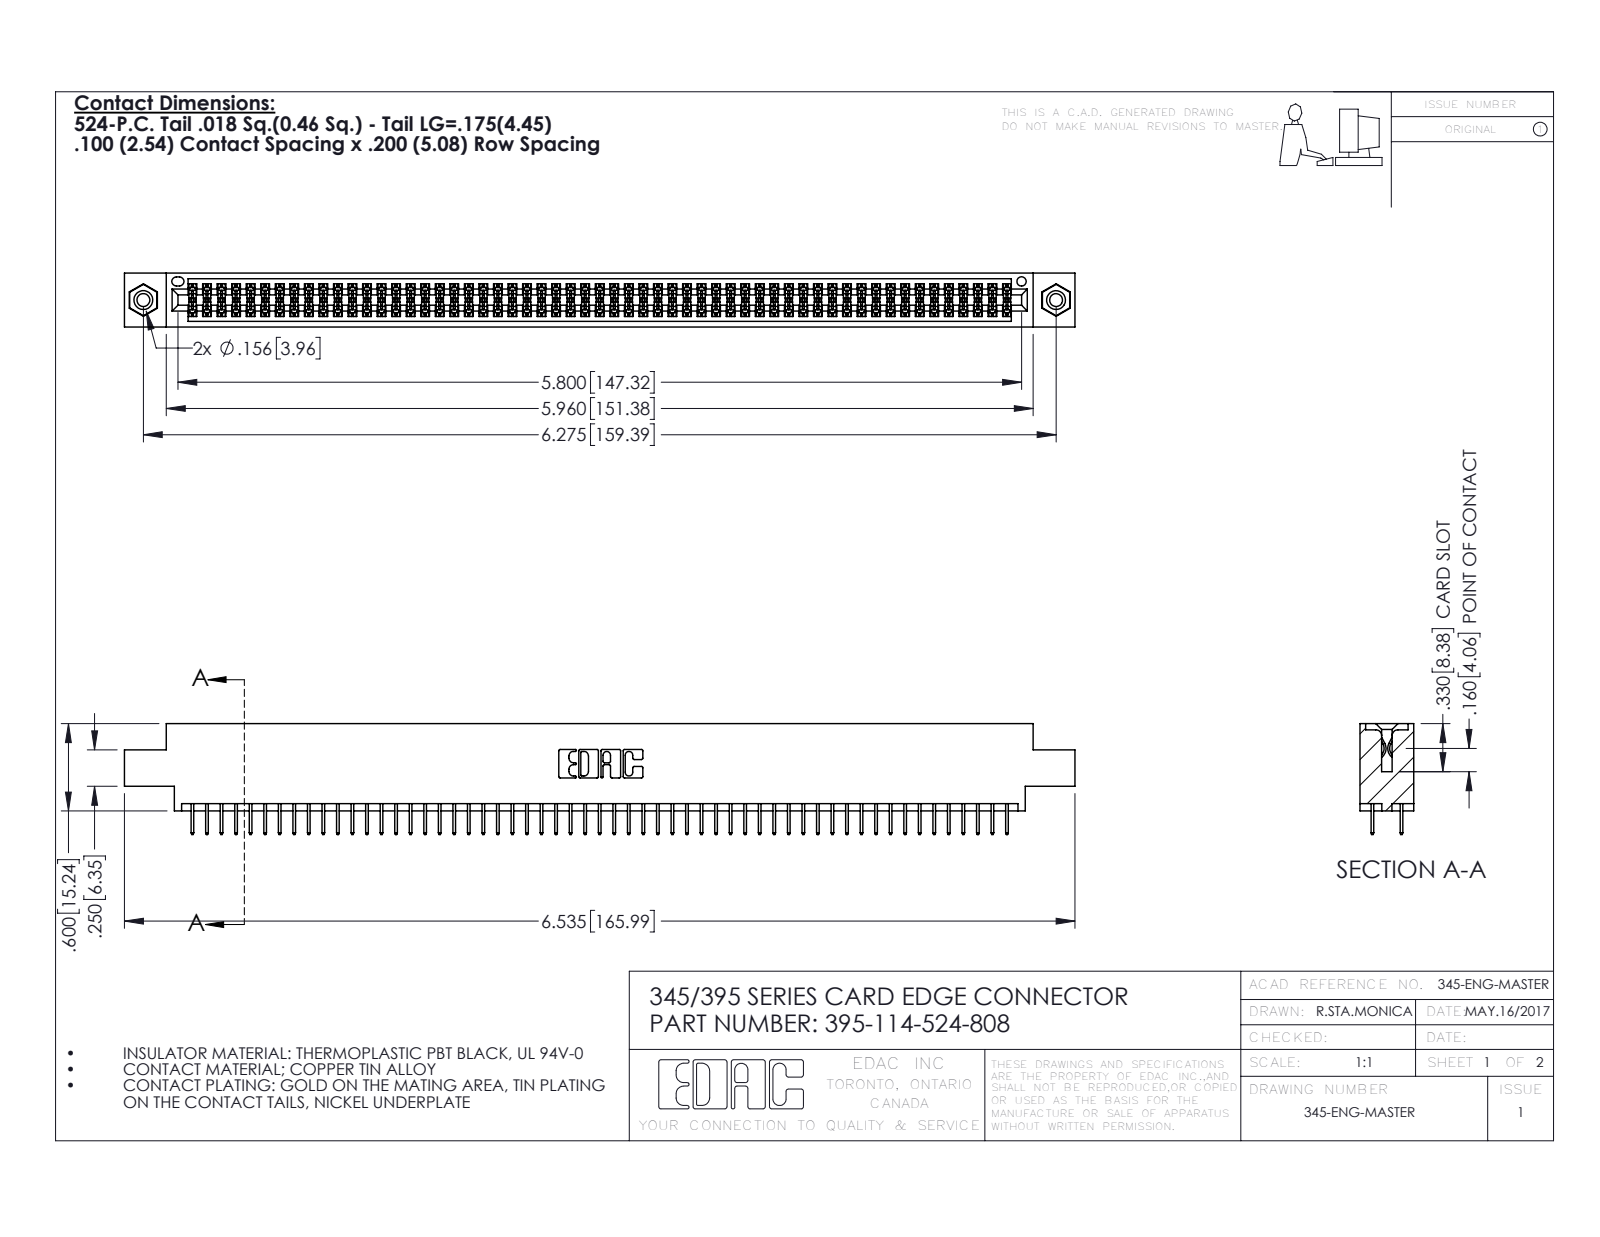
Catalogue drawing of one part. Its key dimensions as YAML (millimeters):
part_name: "345-250-001_345-250-003-102; 395-114-524-808; 345 Part_0.170 Offset - 0.156 Dia-TI; 345-292-001_345-293-124"
step_written_by: "SolidWorks 2016 (CONFIG_CONTROL_DESIGN)"
units: millimeters
bodies: {solids: 117, faces: 6346, planar: 4562, cylindrical: 1768, other: 16}
overall_size: [166, 19.4, 9.4]
volume: 16000
surface_area: 23600
round_holes:
  - {diameter: 2.3, count: 2}
  - {diameter: 3.2, count: 2}
  - {diameter: 4, count: 2}
  - {diameter: 1.6, count: 1}
round_bosses_or_shafts:
  - {diameter: 3.9, count: 2}
partial_cylinders:
  - {radius: 0.2, count: 171}
  - {radius: 0.3, count: 22}
  - {radius: 0.2, count: 6}
  - {radius: 0.8, count: 6}
  - {radius: 0.7, count: 3}
  - {radius: 0.4, count: 2}
  - {radius: 0.5, count: 2}
  - {radius: 0.6, count: 2}
face_to_face_distances: [1.8, 7.6, 9.4, 5.1, 2.5, 6.9, 0.6, 5.7, 1.8, 4.4]
hole_center_spacings: [6.9, 153.4, 159.4]
